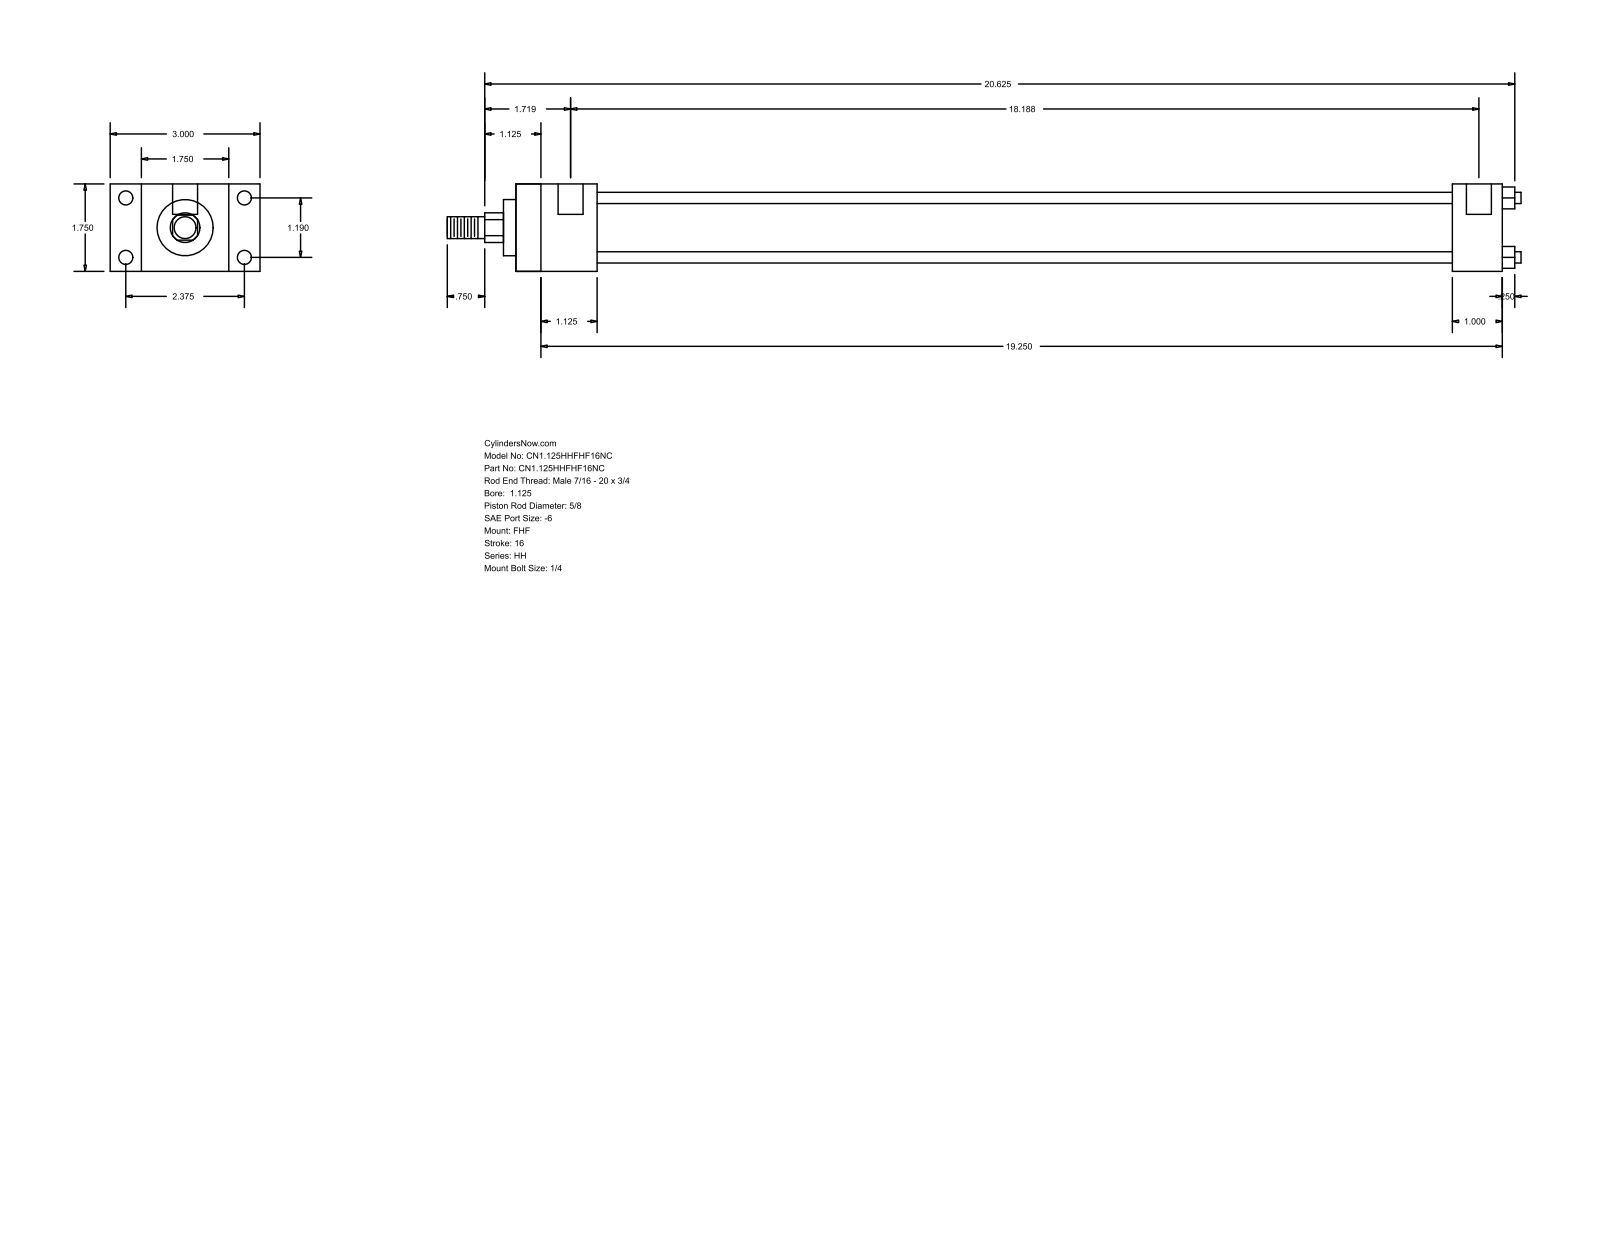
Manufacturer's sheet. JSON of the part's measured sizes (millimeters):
{"part_name": "HH_FHF__0112_0.625", "step_written_by": "GSSL Pune (CONFIG_CONTROL_DESIGN)", "units": "millimeters", "bodies": {"solids": 0, "faces": 88, "planar": 60, "cylindrical": 28, "other": 0}, "overall_size": [546.1, 76.2, 44.45], "round_holes": [[5.56, 4], [7.14, 4], [12.7, 2]], "round_bosses_or_shafts": [[5.71, 4], [34.92, 1], [28.57, 1], [15.88, 1], [11.11, 1]], "partial_cylinders_radius": [[7.54, 1]], "face_to_face_distances": [44.46, 15.87, 60.33, 41.27, 76.2, 501.64, 460.37, 25.4, 476.24, 434.97], "hole_center_spacings": [30.22, 60.32, 67.47, 458.79, 3.17, 461.96]}
